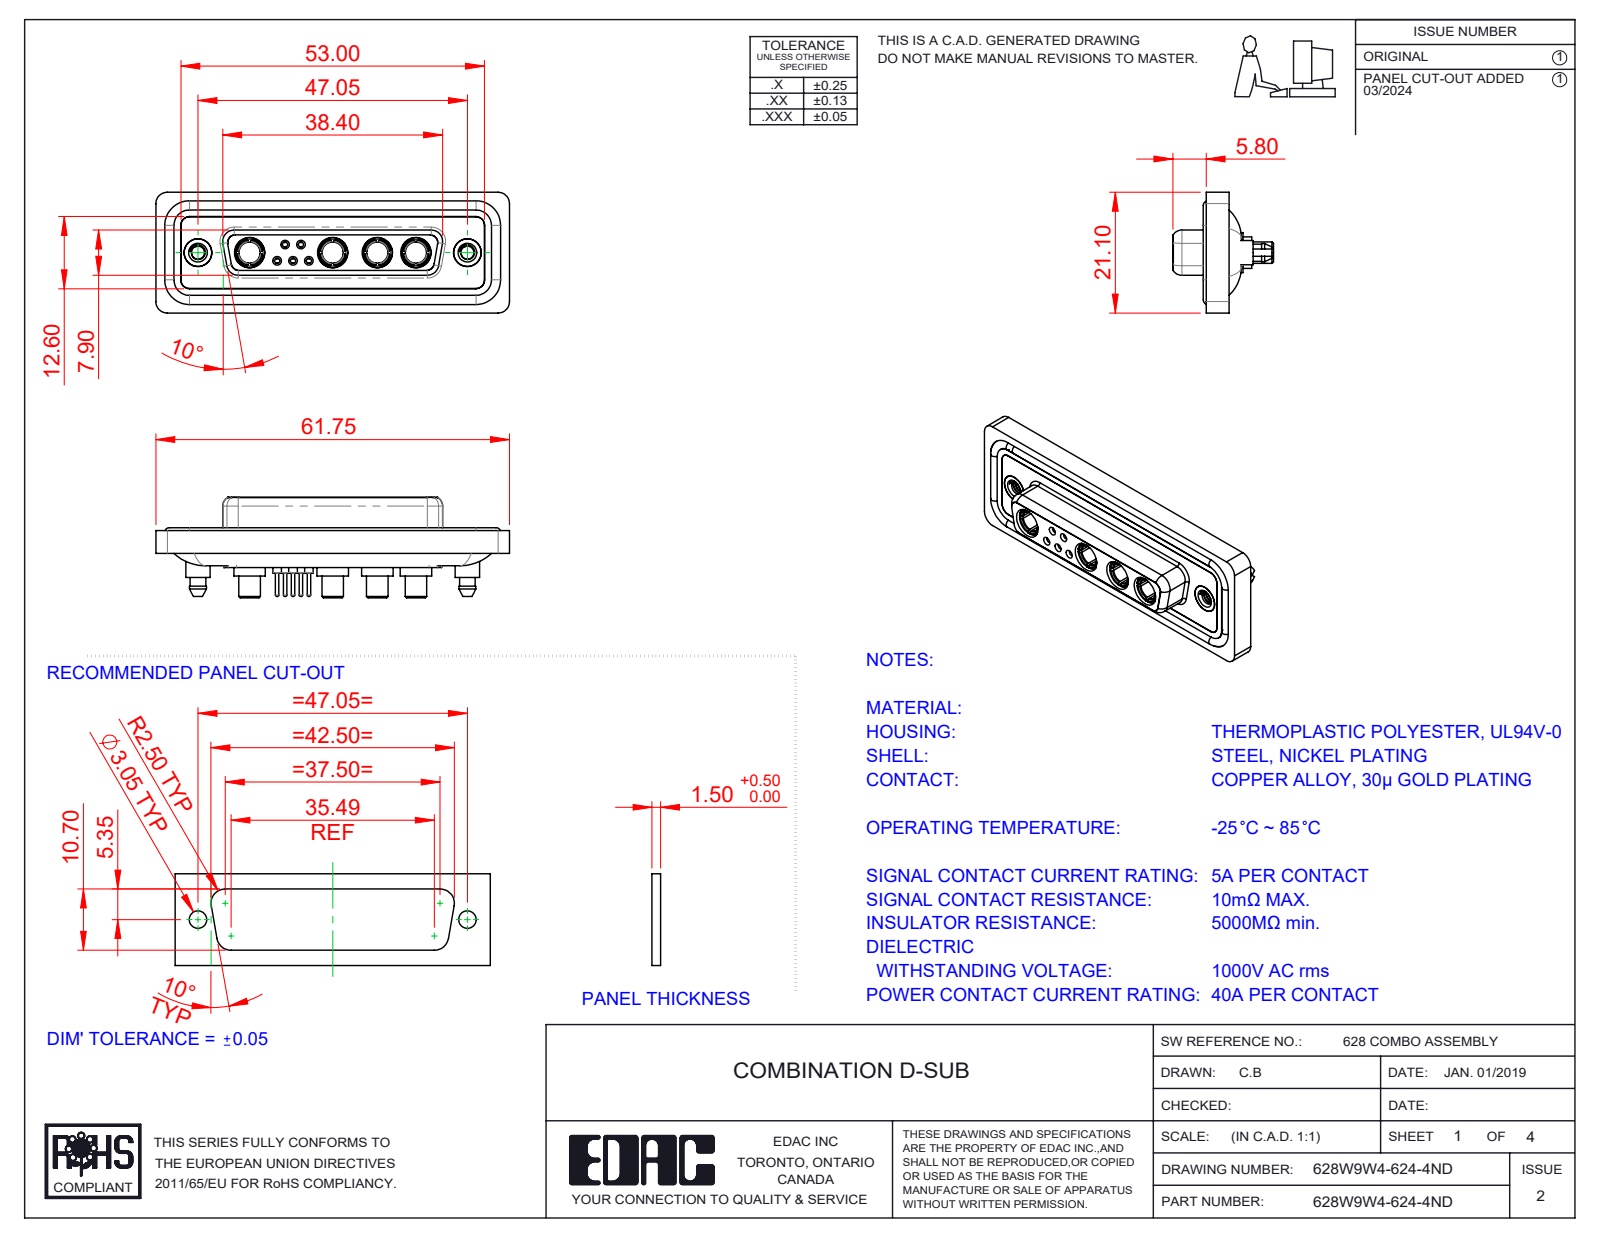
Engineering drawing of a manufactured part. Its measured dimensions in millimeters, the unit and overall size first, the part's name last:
Units: millimetres
Overall size (bounding box): 61.75 × 21.1 × 17.55
Round holes (diameter × count): ⌀4.85 ×6, ⌀0.9 ×5, ⌀1.1 ×5, ⌀1.5 ×5, ⌀2 ×5, ⌀3.7 ×4, ⌀5.3 ×4, ⌀1.6 ×3, ⌀1.7 ×2, ⌀2.26 ×2, ⌀4 ×2, ⌀4.05 ×2
Round bosses / shafts (diameter × count): ⌀1.6 ×6, ⌀2.2 ×5, ⌀0.6 ×5, ⌀5.5 ×4, ⌀5.2 ×4, ⌀4.96 ×4, ⌀4.75 ×4, ⌀3.75 ×4
Partial cylindrical surfaces — rounded edges, fillets, slot ends (radius × count): R1.5 ×24, R2 ×18, R1.6 ×10, R1.35 ×8, R0.25 ×4, R0.5 ×4, R0.6 ×4, R0.65 ×4
Main face-to-face distances: 0.4, 1.8, 7.45, 5.65, 0.5, 7.05, 6.6, 1.6, 1.1, 2.9
Hole centre spacings: 3.16, 2.77, 5.03, 2.76, 4.4, 5.02, 5.54, 5.73
Volume: 8 432 mm³ · Surface area: 13 945 mm²
Bodies: 20 solids, 1023 faces (312 planar, 423 cylindrical, 288 other)
Part name (STEP PRODUCT): Power Socket_40A S; 628Combo Shell Rear_25 Contacts; 628Combo Waterproof Housing_25 Contacts; 628Combo Shell Front_25 Contacts (+5 more)
STEP written by: SolidWorks 2023 (CONFIG_CONTROL_DESIGN)
